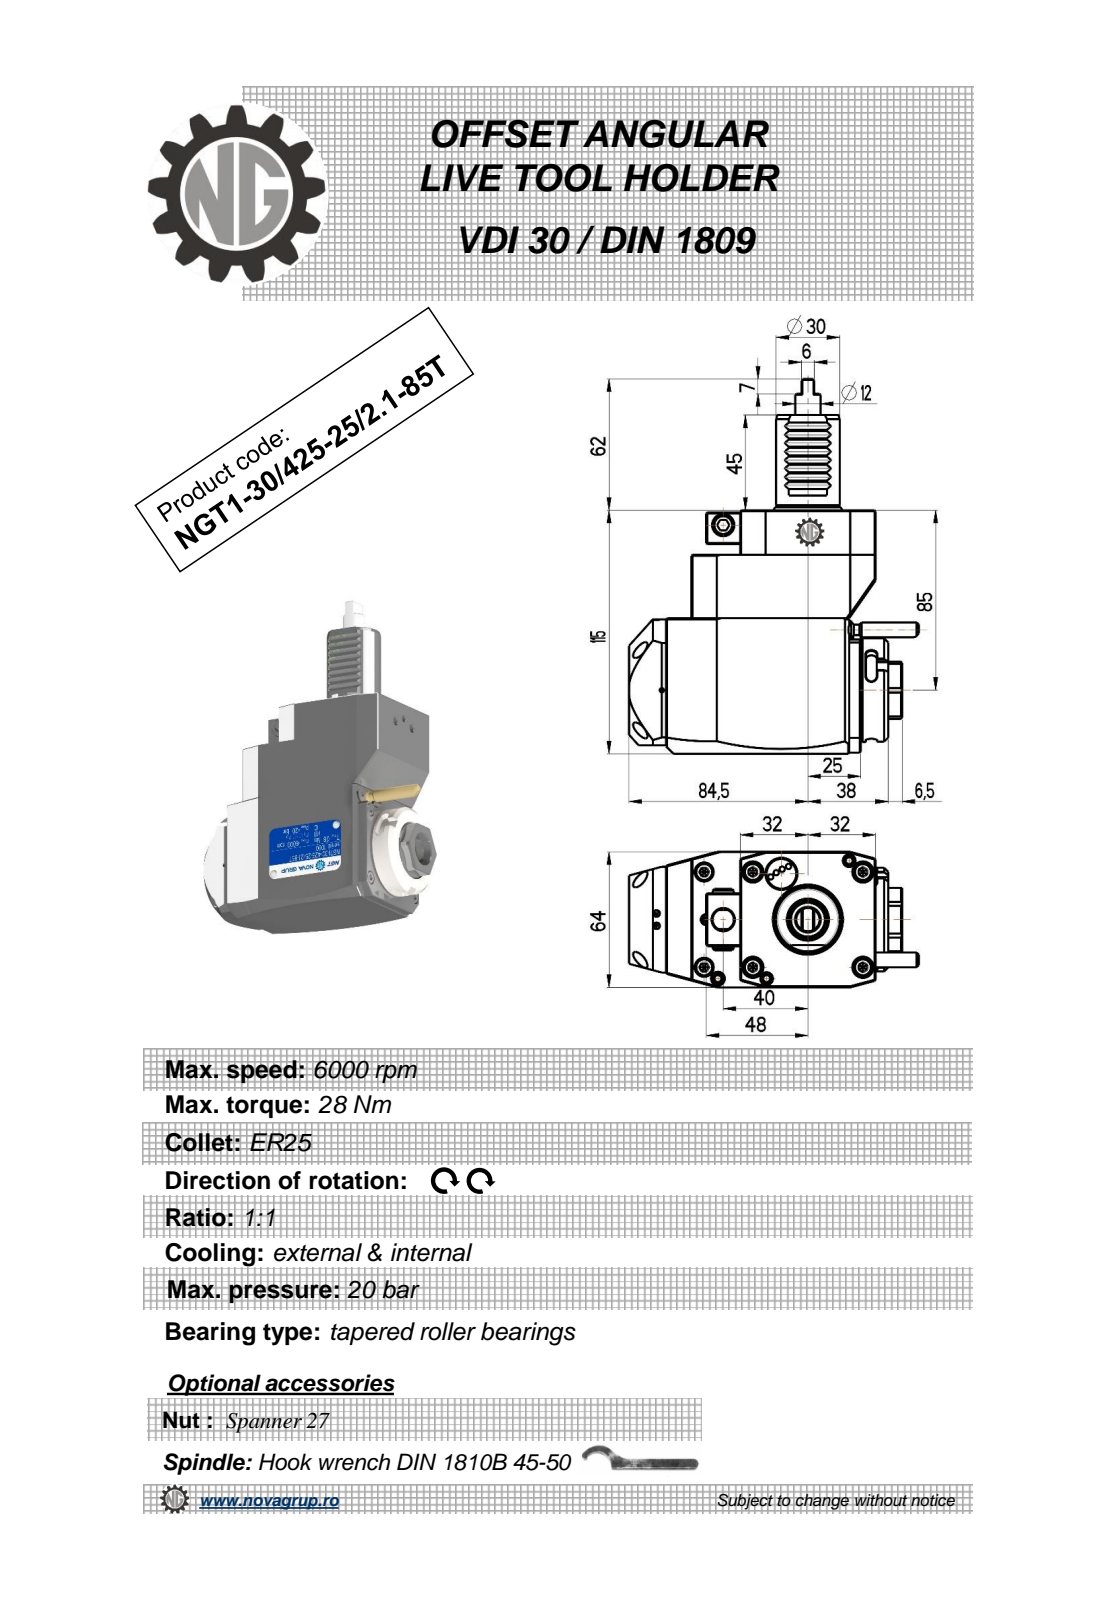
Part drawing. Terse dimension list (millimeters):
name: NGT1_30_425_25_1_1_85T
written by: PRO/ENGINEER BY PARAMETRIC TECHNOLOGY CORPORATION, 2010280 (CONFIG_CONTROL_DESIGN)
unit: mm
bodies: 1 solid, 325 faces (187 planar, 68 cylindrical, 70 other)
size: 177 × 136.88 × 64
volume: 705 879 mm³; area: 58 642 mm²
holes: 1× ⌀2.5, 1× ⌀3, 1× ⌀8.5, 1× ⌀9.5, 1× ⌀10, 1× ⌀18
bosses: 2× ⌀8.96, 1× ⌀49, 1× ⌀42, 1× ⌀30, 1× ⌀12, 1× ⌀10, 1× ⌀7, 1× ⌀5
rounds: 8× R0.3, 6× R2.5, 2× R0.8, 2× R180, 1× R4.5, 1× R15, 1× R21.5, 1× R33.5
face distances: 64, 115, 7, 80, 87, 6, 29.5, 94, 21, 116.5
hole spacings: 34.25, 51.62, 76.5
